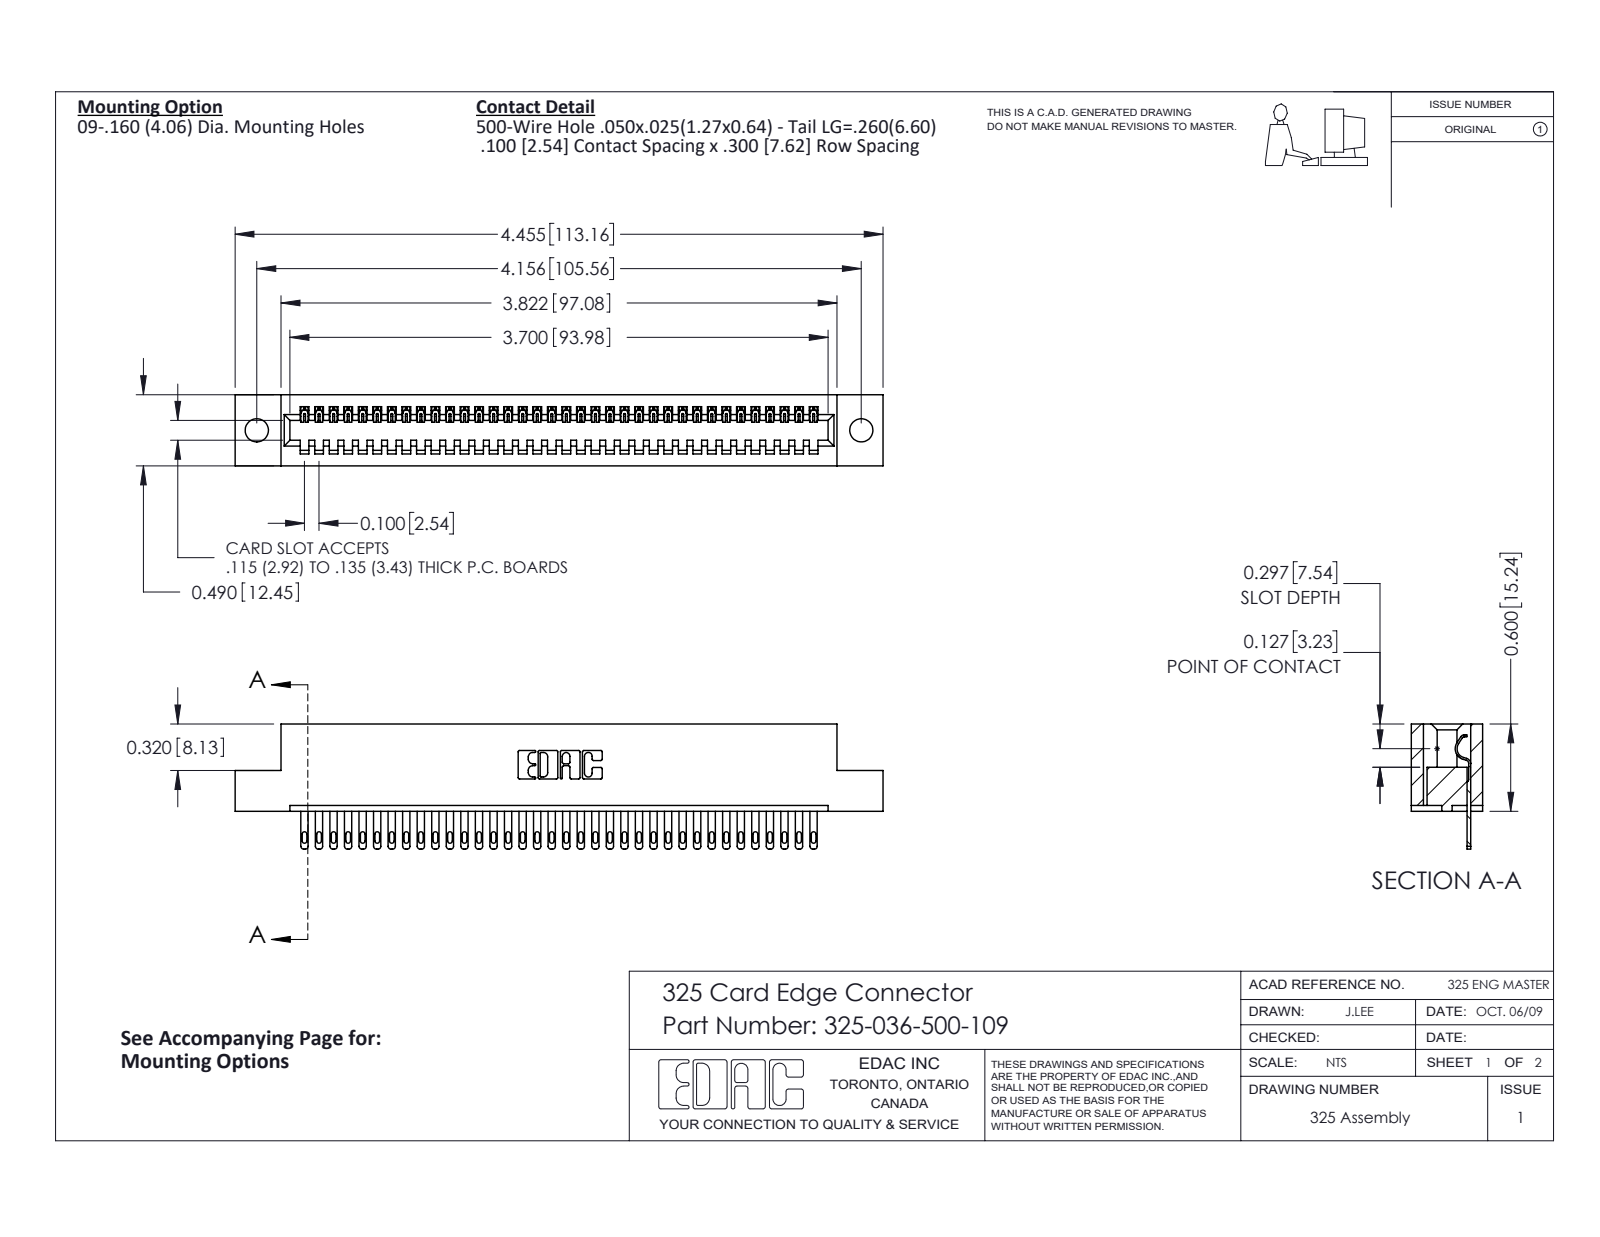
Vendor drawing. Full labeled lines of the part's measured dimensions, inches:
Part name (STEP PRODUCT): 325-292-001_325-293-100; 325 Part_.160 TH; 325-036-500-109
STEP written by: SolidWorks 2016 (CONFIG_CONTROL_DESIGN)
Units: inches
Bodies: 37 solids, 2058 faces (1366 planar, 692 cylindrical, 0 other)
Overall size (bounding box): 4.455 × 0.86 × 0.49
Volume: 0.861 in³ · Surface area: 23.7 in²
Round holes (diameter × count): ⌀0.16 ×2
Partial cylindrical surfaces — rounded edges, fillets, slot ends (radius × count): R0.006 ×72, R0.016 ×72, R0.02 ×72, R0.01 ×22, R0.007 ×6, R0.031 ×6, R0.026 ×3, R0.014 ×1
Main face-to-face distances: 0.083, 0.407, 0.49, 0.3, 0.107, 0.383, 0.025, 0.325, 0.56, 0.04
Hole centre spacings: 4.156
